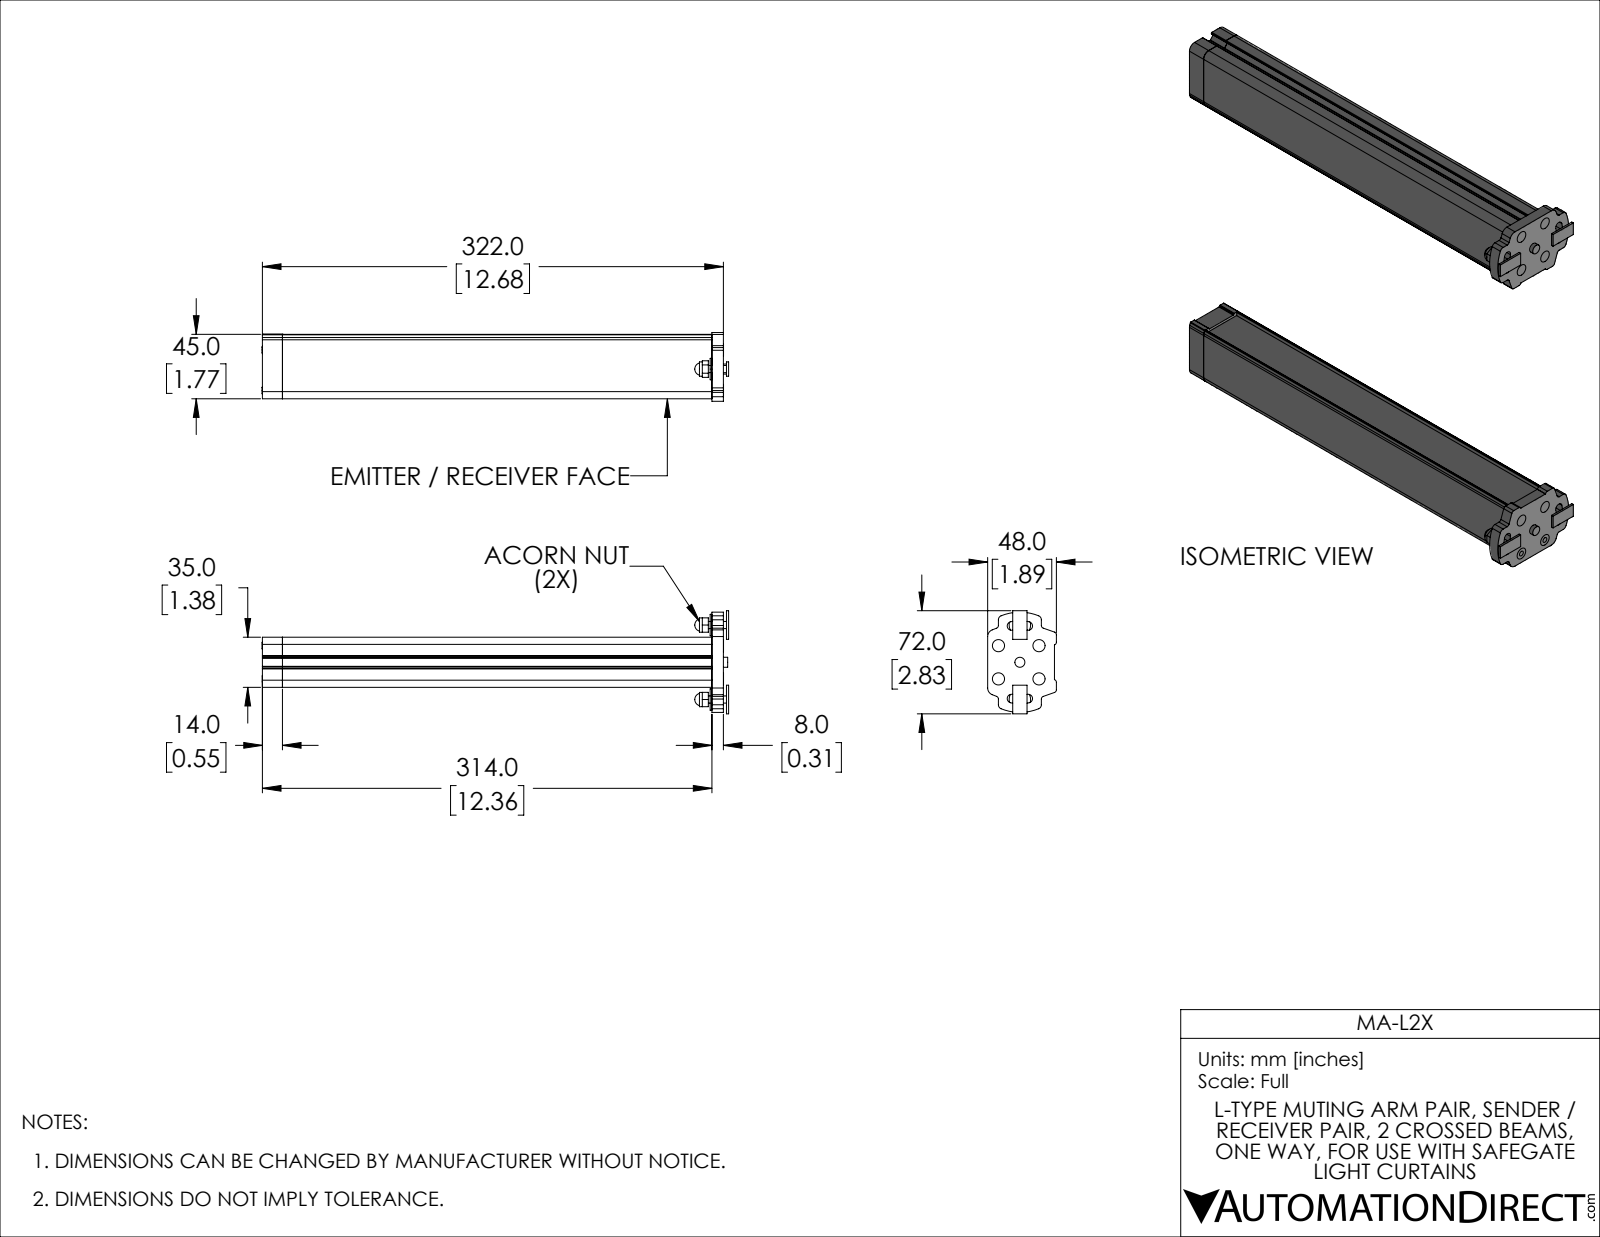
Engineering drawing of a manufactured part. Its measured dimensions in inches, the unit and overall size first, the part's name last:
Units: inches
Overall size (bounding box): 12.83 × 5.902 × 2.835
Round holes (diameter × count): ⌀0.142 ×8, ⌀0.15 ×8, ⌀0.209 ×4, ⌀0.217 ×4
Round bosses / shafts (diameter × count): ⌀0.236 ×8, ⌀0.118 ×8, ⌀0.591 ×4, ⌀0.394 ×4, ⌀0.197 ×4, ⌀0.276 ×2
Partial cylindrical surfaces — rounded edges, fillets, slot ends (radius × count): R0.02 ×80, R0.012 ×64, R0.079 ×16, R0.118 ×16, R0.197 ×12, R0.008 ×4, R0.019 ×2, R0.019 ×2
Main face-to-face distances: 1.378, 0.118, 2.576, 1.571, 4.193, 2.457, 2.694, 0.083, 0.036, 0.082
Hole centre spacings: 0.773, 0.817, 0.913, 1.114, 1.441, 1.571, 1.593, 3.649
Volume: 57.96 in³ · Surface area: 296.8 in²
Bodies: 36 solids, 676 faces (358 planar, 294 cylindrical, 24 other)
Part name (STEP PRODUCT): MA-L2X; MA-2LX-left; MA-2LX-right
STEP written by: SolidWorks 2019 (AUTOMOTIVE_DESIGN)
